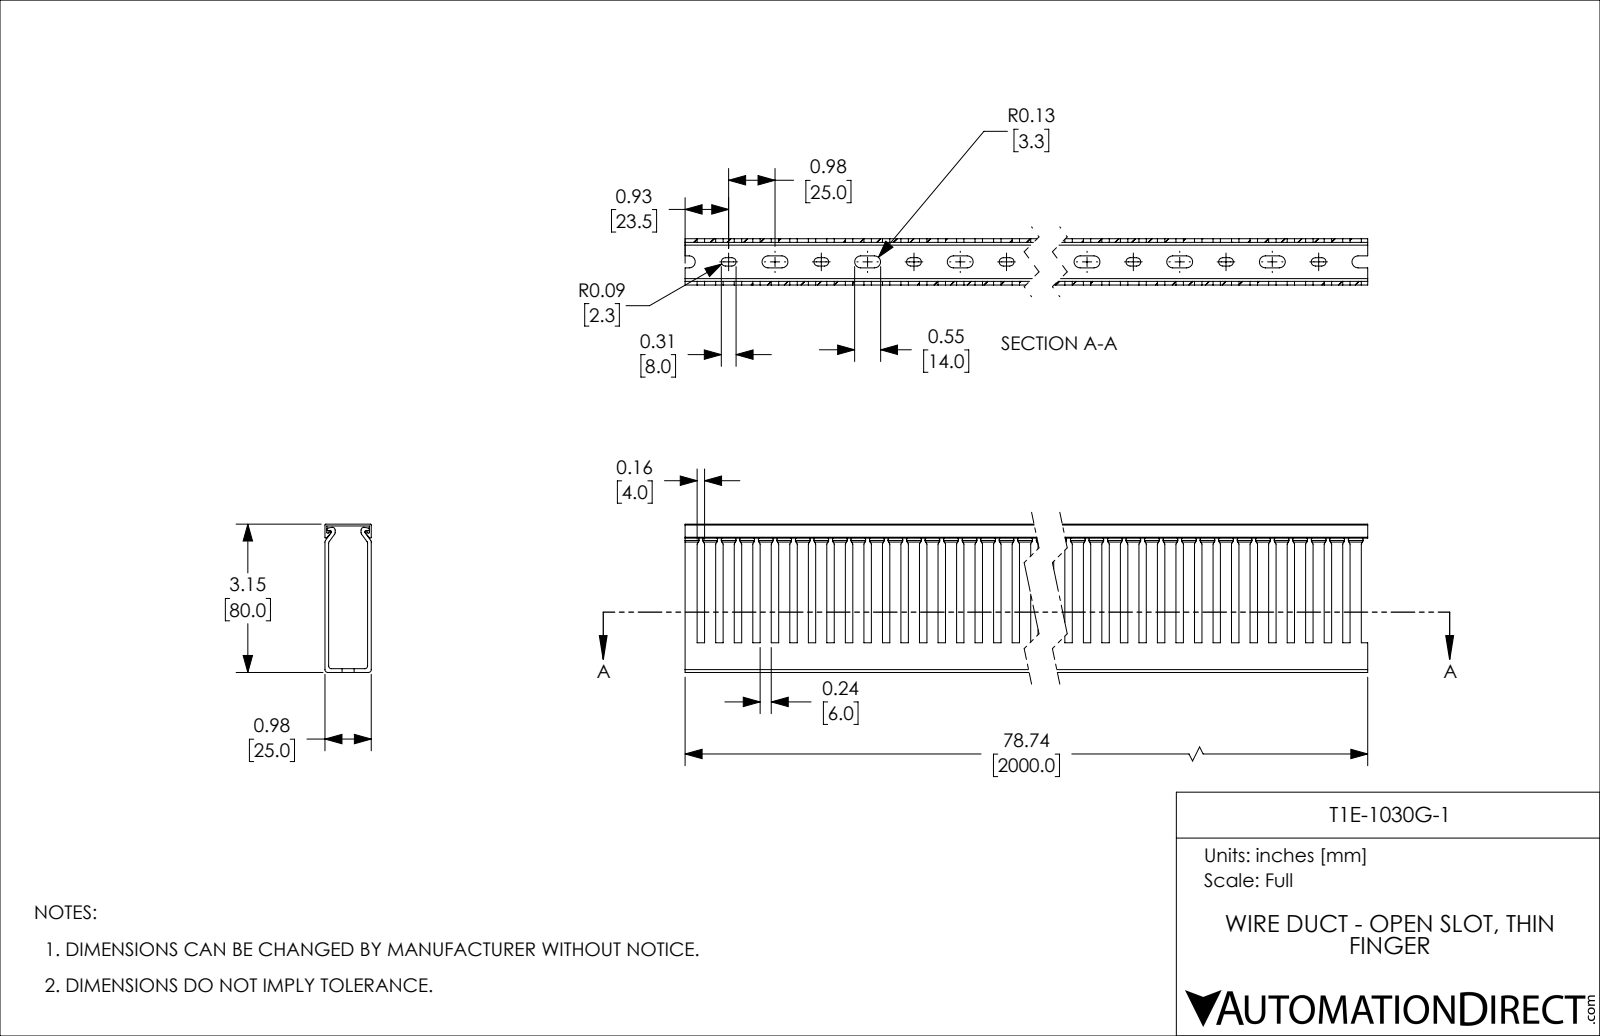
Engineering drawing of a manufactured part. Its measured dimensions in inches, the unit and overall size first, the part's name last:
Units: inches
Overall size (bounding box): 78.74 × 3.15 × 0.984
Partial cylindrical surfaces — rounded edges, fillets, slot ends (radius × count): R0.089 ×80, R0.128 ×80, R0.059 ×12, R0.02 ×8, R0.03 ×6
Main face-to-face distances: 0.079, 0.906, 0.984, 0.827, 0.039, 3.15, 3.11, 3.031, 3.071, 0.945
Volume: 48.91 in³ · Surface area: 1 386 in²
Bodies: 2 solids, 945 faces (514 planar, 431 cylindrical, 0 other)
Part name (STEP PRODUCT): T1E-1030G-1
STEP written by: SolidWorks 2021 (CONFIG_CONTROL_DESIGN)
